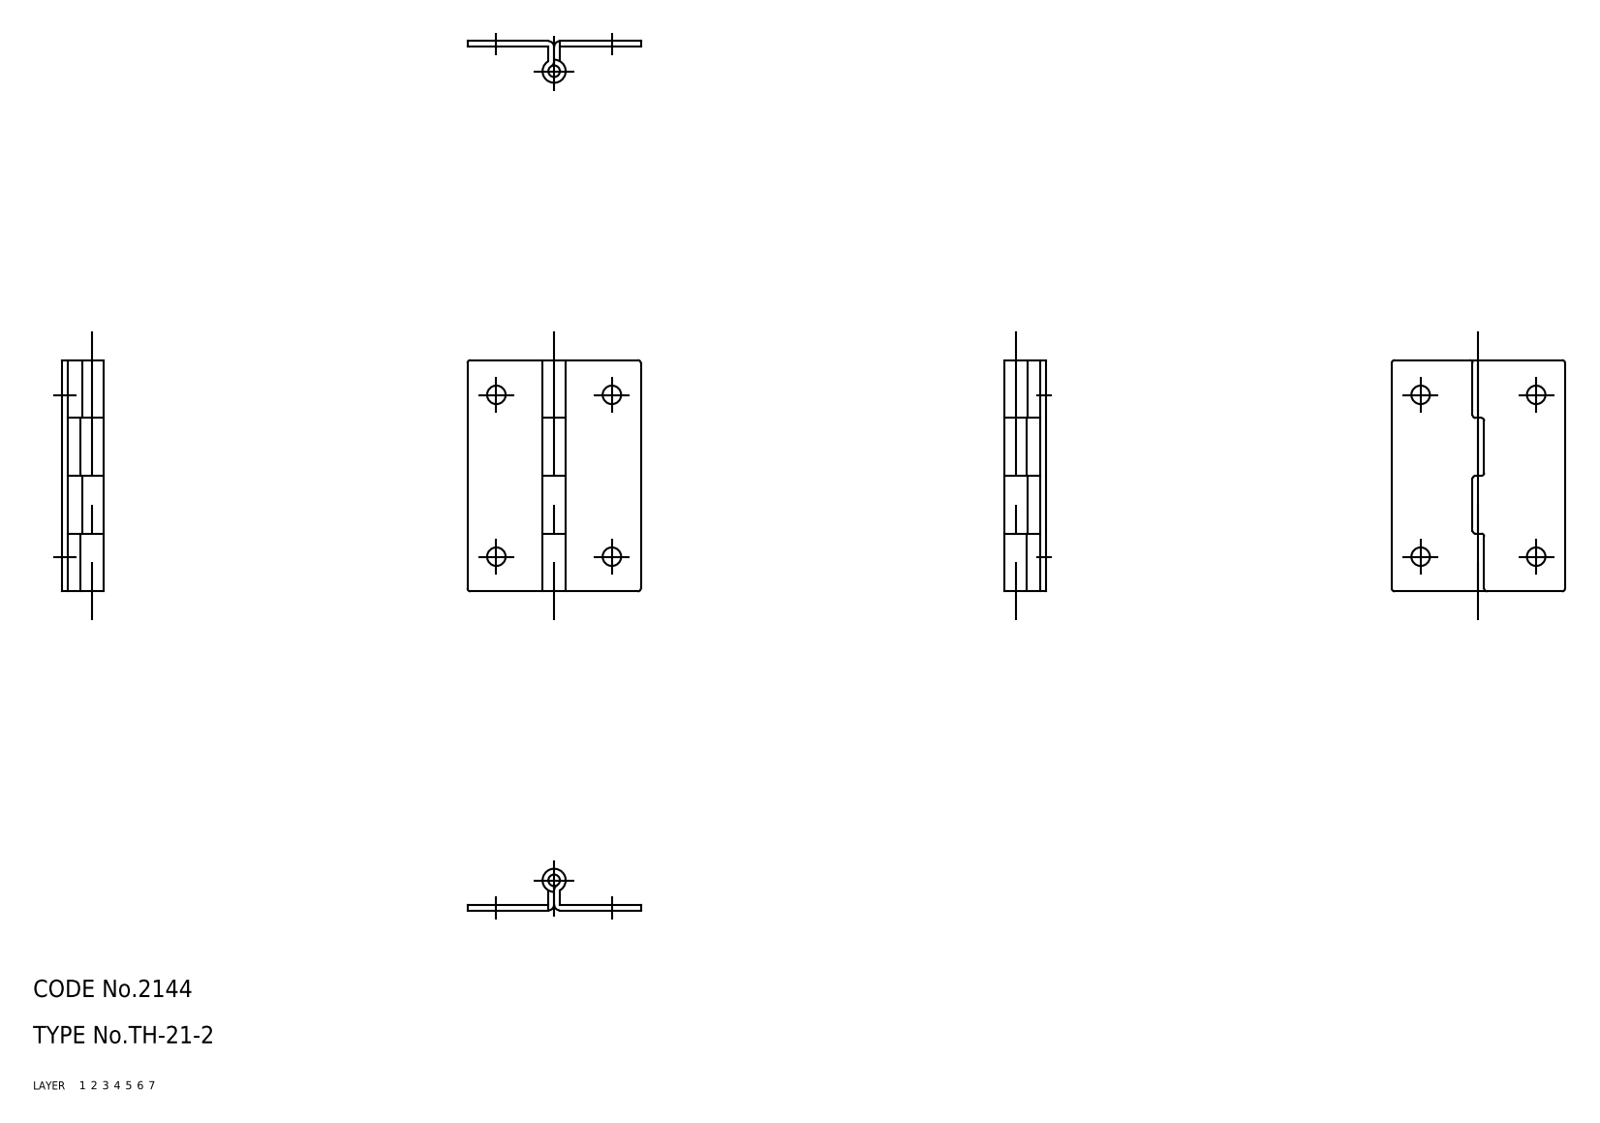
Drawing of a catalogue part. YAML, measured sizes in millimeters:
part_name: "shaft; hinge piece_B; hinge piece_A; TH_21_2_6211_36"
step_written_by: "CADfix (AUTOMOTIVE_DESIGN)"
units: millimeters
bodies: {solids: 3, faces: 66, planar: 0, cylindrical: 0, other: 66}
overall_size: [40, 30, 7.2]
volume: 1710
surface_area: 3782
